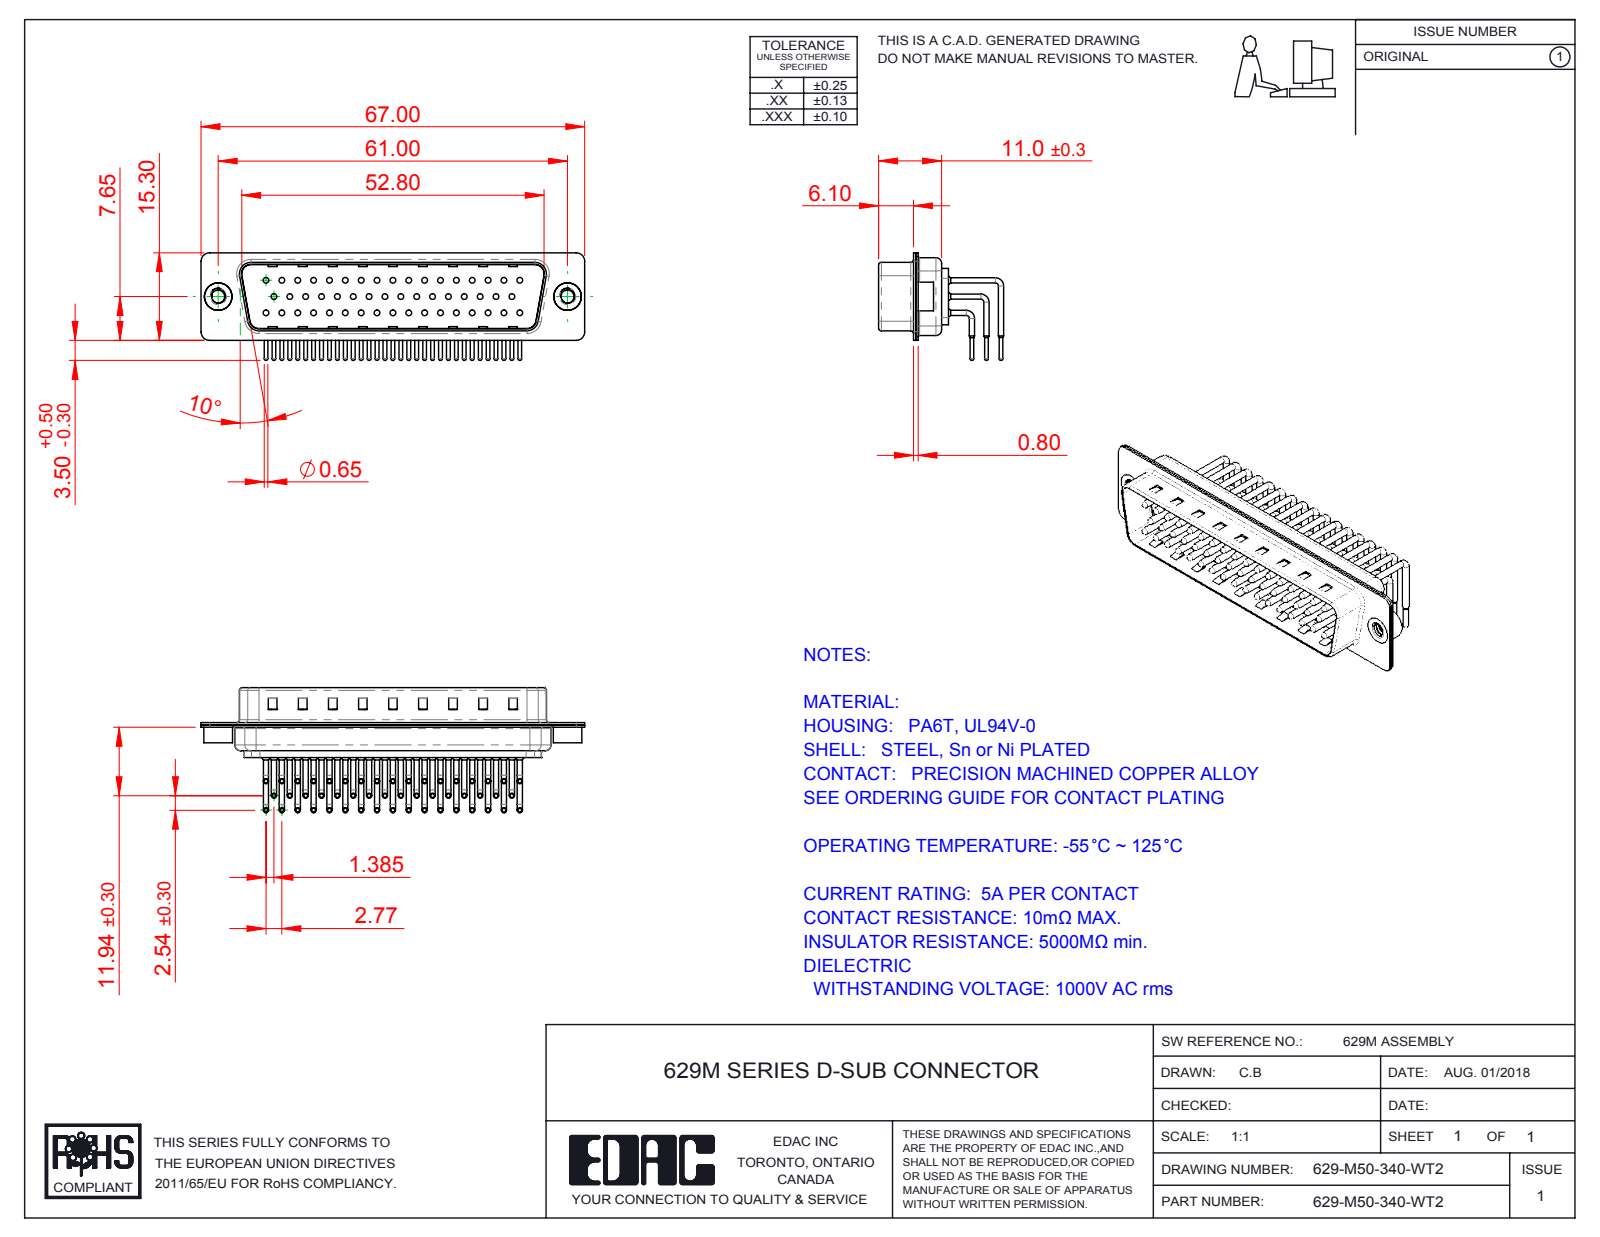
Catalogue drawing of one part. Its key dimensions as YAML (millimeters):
part_name: "629M Shell Front_50 Contacts; 629M Housing_50 Contacts; 629M Shell Rear_50 Contacts; 629M Contact Row 1_50 Contacts (+4 more)"
step_written_by: "SolidWorks 2016 (CONFIG_CONTROL_DESIGN)"
units: millimeters
bodies: {solids: 55, faces: 5912, planar: 3403, cylindrical: 1941, other: 568}
overall_size: [67, 21.83, 18.8]
volume: 4991
surface_area: 12894
round_holes:
  - {diameter: 1, count: 50}
  - {diameter: 1.7, count: 50}
  - {diameter: 2, count: 50}
  - {diameter: 2.26, count: 2}
  - {diameter: 4, count: 2}
  - {diameter: 4.8, count: 2}
round_bosses_or_shafts:
  - {diameter: 0.9, count: 100}
  - {diameter: 1.5, count: 50}
  - {diameter: 0.65, count: 50}
  - {diameter: 5, count: 2}
  - {diameter: 4.9, count: 2}
partial_cylinders:
  - {radius: 1.01, count: 50}
  - {radius: 1.5, count: 16}
  - {radius: 2, count: 12}
  - {radius: 0.5, count: 8}
  - {radius: 1.6, count: 8}
  - {radius: 0.25, count: 4}
  - {radius: 0.6, count: 4}
  - {radius: 0.65, count: 4}
face_to_face_distances: [0.4, 11.55, 5.7, 6.1, 12.38, 0.83, 0.82, 12.37, 13.2, 4.2]
hole_center_spacings: [2.77, 3.16, 5.54, 8.31, 11.08, 13.85, 16.62, 19.39]
